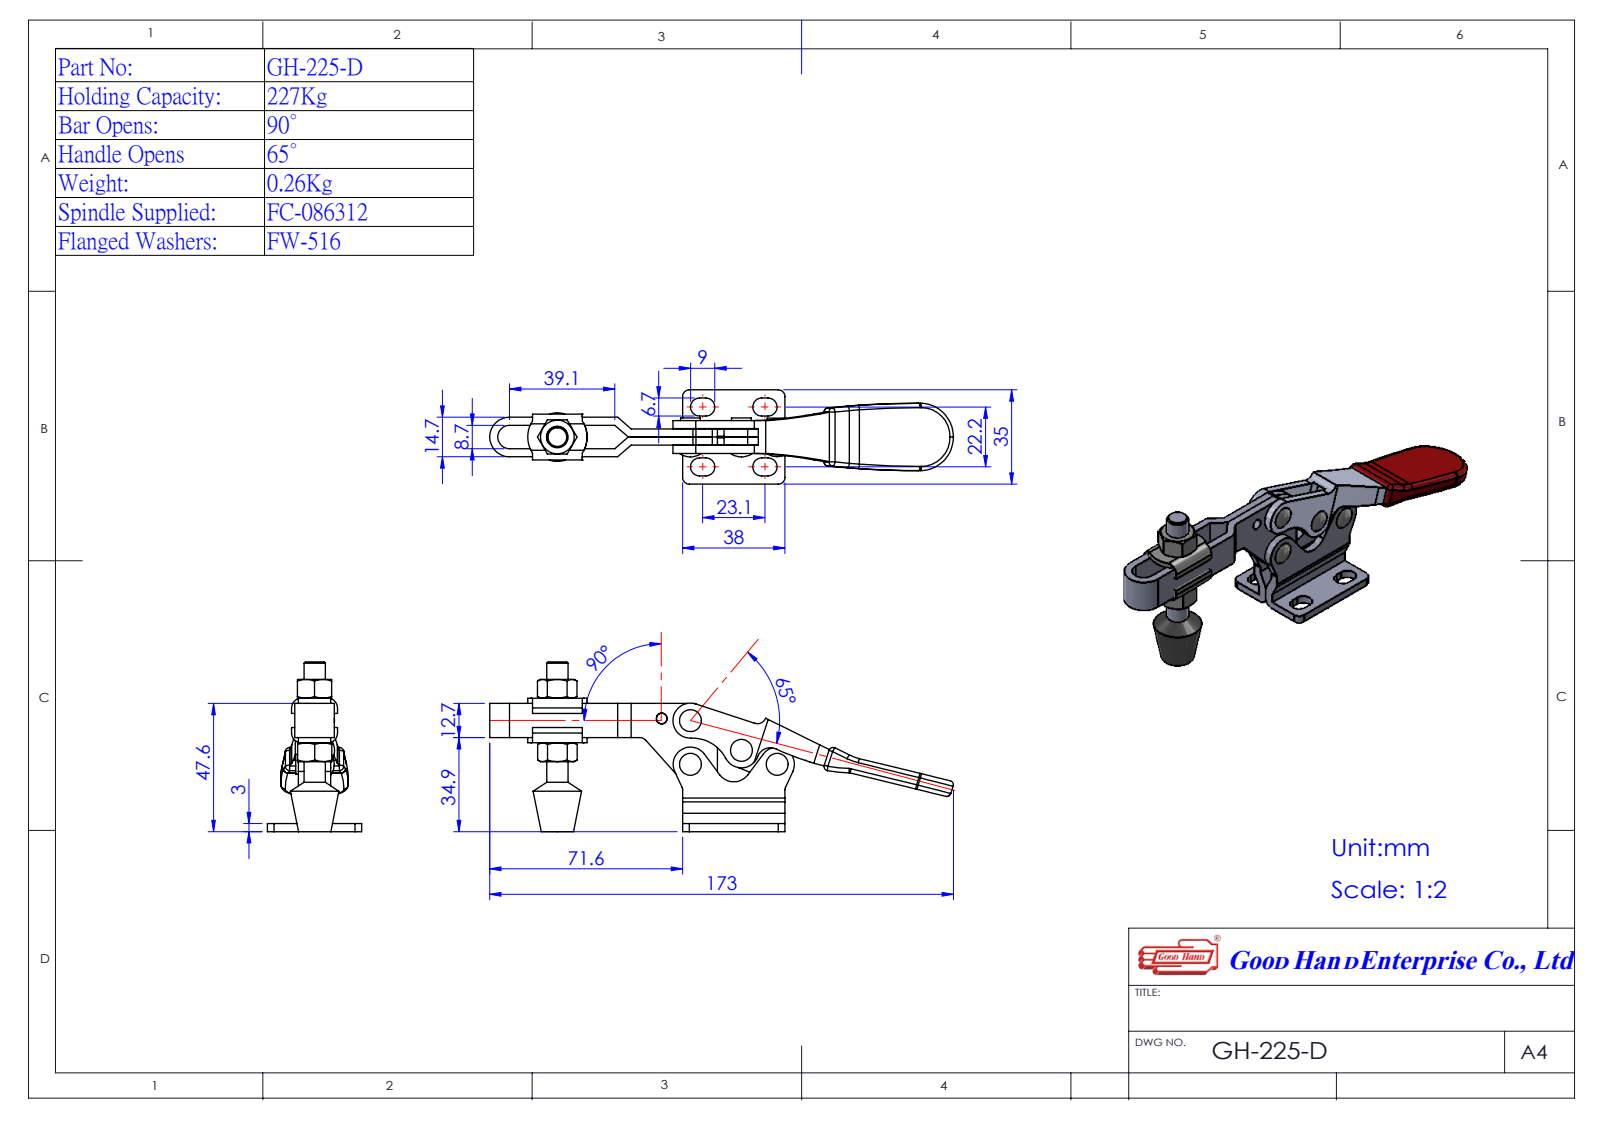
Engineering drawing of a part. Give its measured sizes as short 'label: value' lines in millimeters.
name: Group4^EMC225D; Group5^EMC225D; EMC225D; Group1^EMC225D (+2 more)
written by: SolidWorks 2016 (AUTOMOTIVE_DESIGN)
unit: mm
bodies: 4 solids, 293 faces (130 planar, 136 cylindrical, 27 other)
size: 173.56 × 63 × 35
volume: 27 879 mm³; area: 27 172 mm²
holes: 4× ⌀5
bosses: 4× ⌀7.35, 2× ⌀6.35, 2× ⌀6.3, 1× ⌀7.93, 1× ⌀4
rounds: 11× R3, 8× R3.35, 4× R1.2, 4× R2.5, 4× R3.6, 4× R11.04, 3× R6.4, 3× R6.5
face distances: 3, 6, 3.1, 6.1, 9.1, 3.01, 2.99, 7.35, 4.36, 4.34
hole spacings: 14.25, 16.2, 19.63, 21.9, 32.2, 36.05
